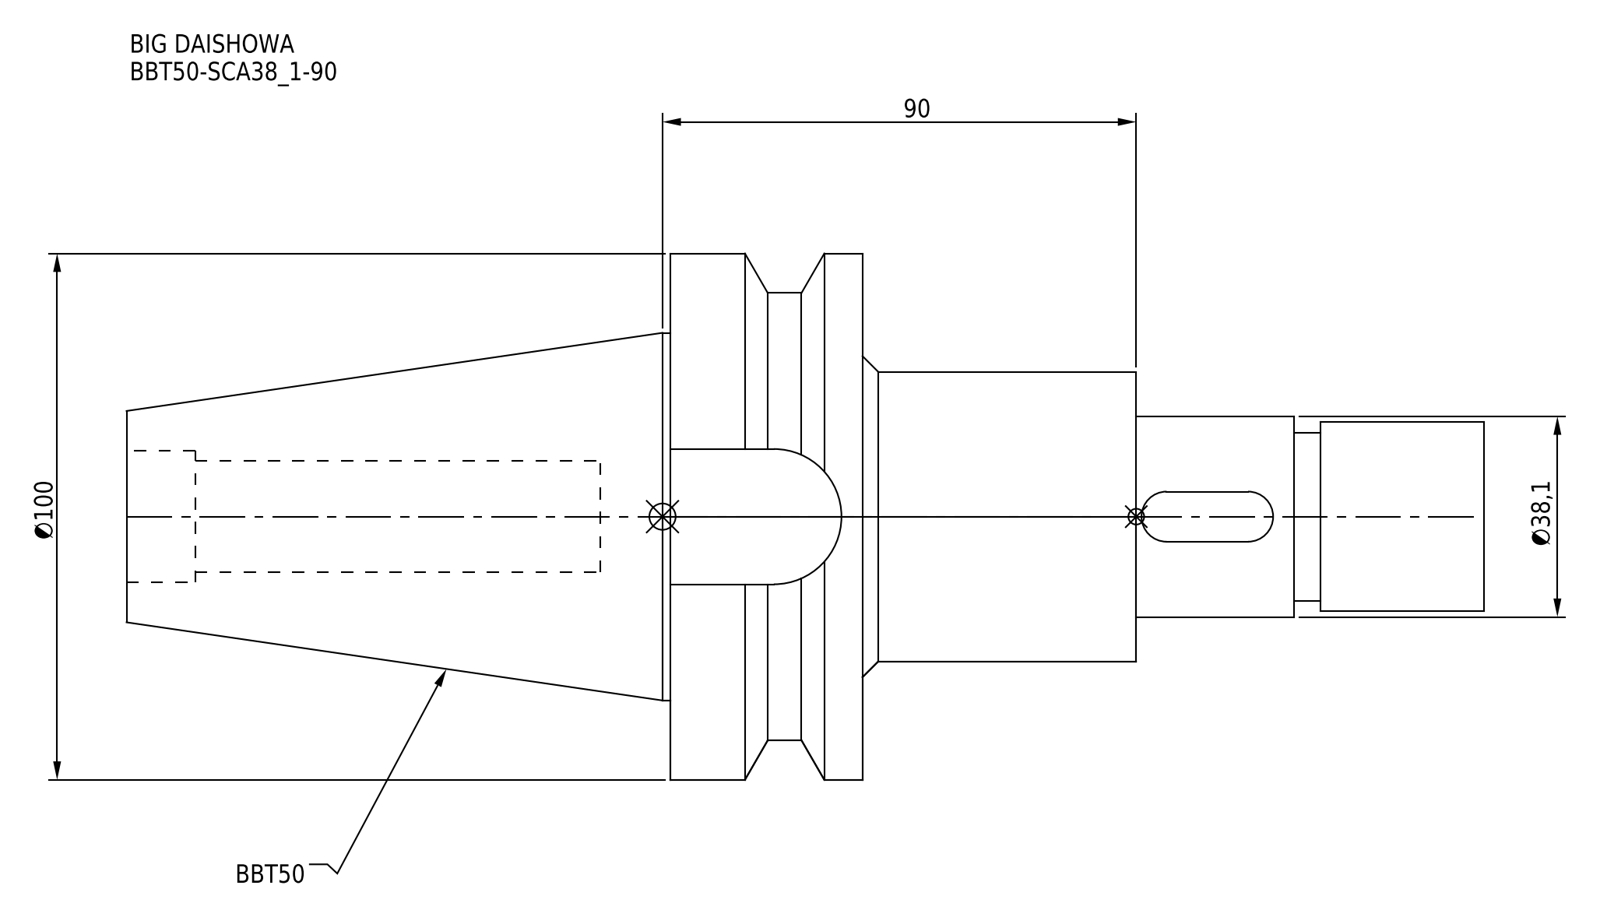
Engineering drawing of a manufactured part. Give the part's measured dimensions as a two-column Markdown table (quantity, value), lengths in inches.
| quantity | value |
| --- | --- |
| part name | BBT50-SCA38_1-90 |
| STEP written by | CREO PARAMETRIC BY PTC INC, 2016380 (AUTOMOTIVE_DESIGN) |
| units | inches |
| bodies | 1 solid, 42 faces (12 planar, 22 cylindrical, 8 other) |
| overall size | 10.15 × 3.937 × 3.937 |
| volume | 41.37 in³ |
| surface area | 105.2 in² |
| round holes (diameter × count) | 0.835 × 1, 0.984 × 1 |
| round bosses / shafts (diameter × count) | 3.937 × 1, 3.346 × 1, 2.75 × 1, 2.165 × 1, 1.5 × 1, 1.417 × 1, 1.26 × 1 |
| partial cylindrical surfaces (radius × count) | 0.187 × 2 |
| main face-to-face distances | 1.437, 2.047, 3.484, 2.598, 4.646, 6.083, 10.15, 7.551, 5.504, 4.067 |
